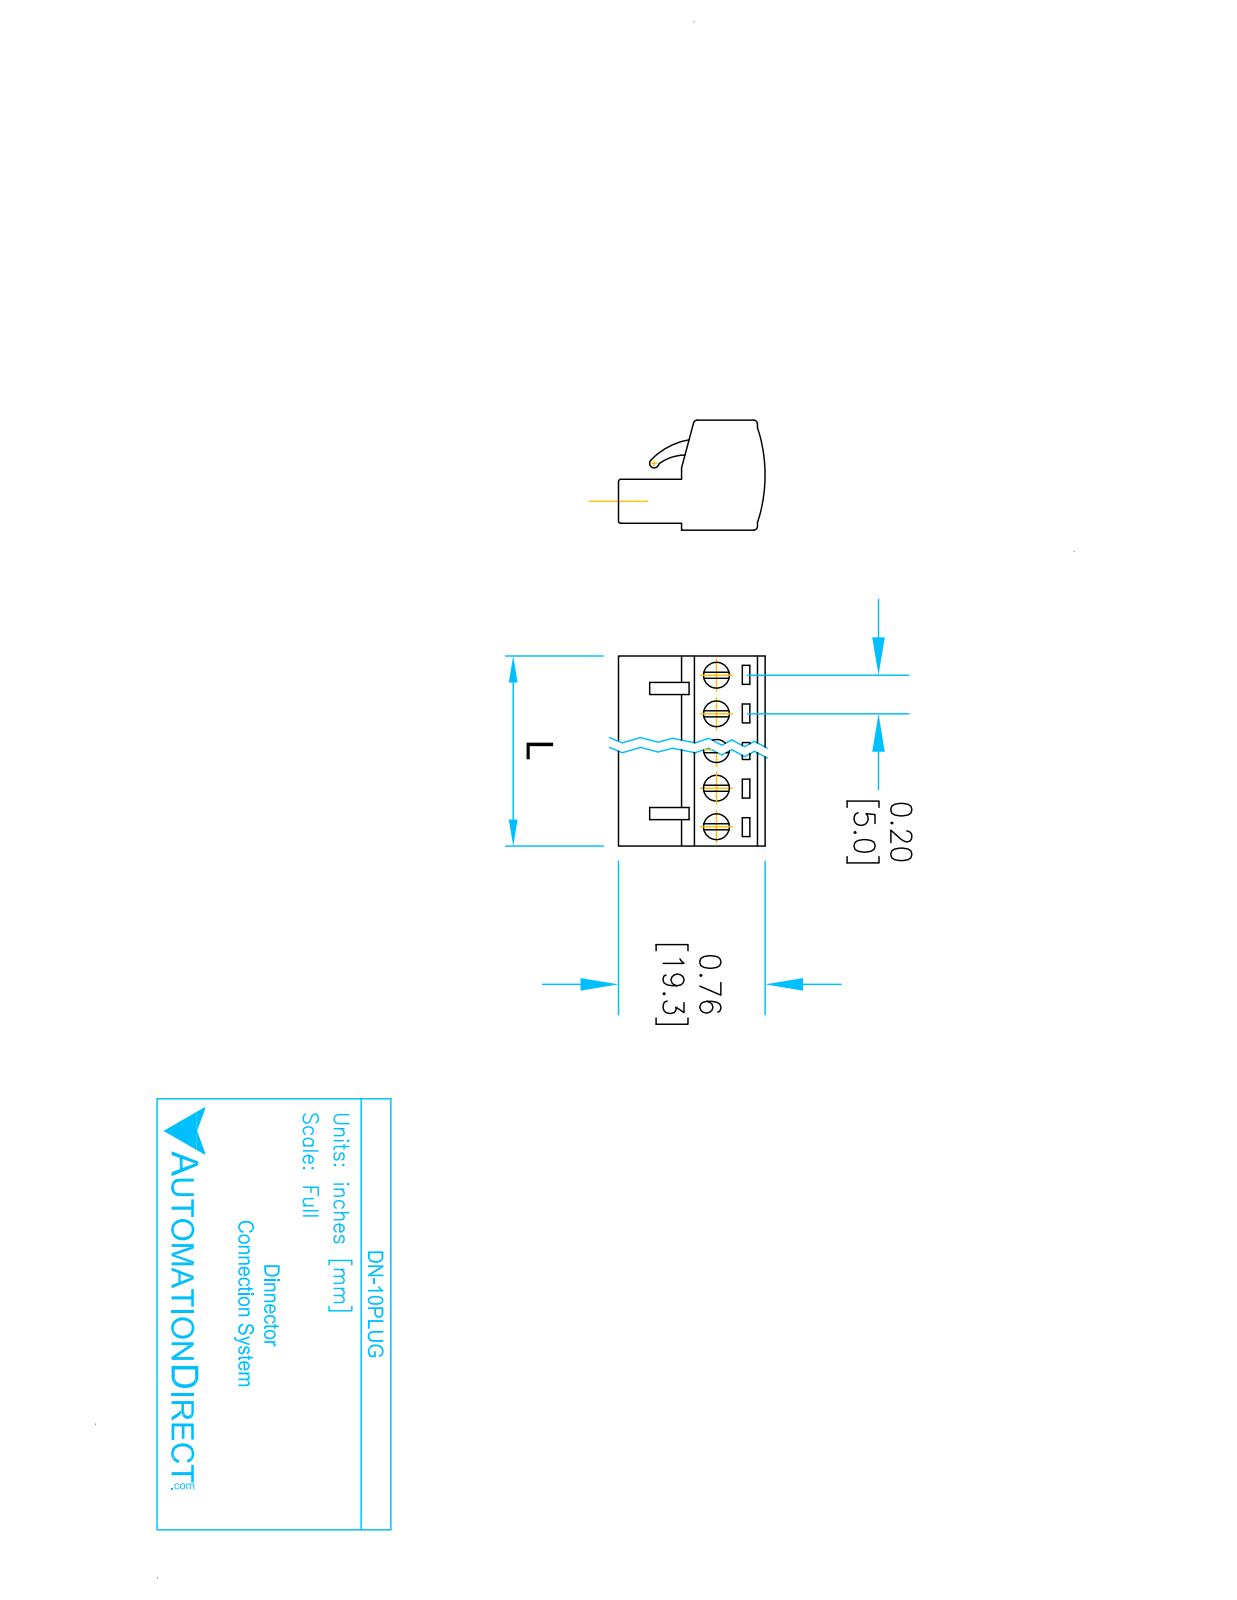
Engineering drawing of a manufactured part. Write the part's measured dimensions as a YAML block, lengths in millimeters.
part_name: "49002_S; 49001_S_49002_SENZA DENTE; 49001_S; 49010_S"
step_written_by: "SolidWorks 2013 (AUTOMOTIVE_DESIGN)"
units: millimeters
bodies: {solids: 9, faces: 914, planar: 643, cylindrical: 221, other: 50}
overall_size: [50.8, 19.3, 14.5]
volume: 8680
surface_area: 9003
round_holes:
  - {diameter: 1.6, count: 10}
  - {diameter: 2.5, count: 10}
  - {diameter: 3.4, count: 10}
  - {diameter: 3.6, count: 10}
round_bosses_or_shafts:
  - {diameter: 3, count: 10}
partial_cylinders:
  - {radius: 2.9, count: 10}
  - {radius: 0.5, count: 3}
  - {radius: 0.3, count: 2}
  - {radius: 0.6, count: 1}
  - {radius: 6, count: 1}
  - {radius: 9, count: 1}
  - {radius: 20.03, count: 1}
face_to_face_distances: [5.08, 10.16, 15.24, 20.32, 25.4, 30.48, 35.56, 6.7, 1, 40.64]
hole_center_spacings: [5.08, 10.16, 15.24, 20.32, 25.4, 30.48, 35.56, 40.64]
